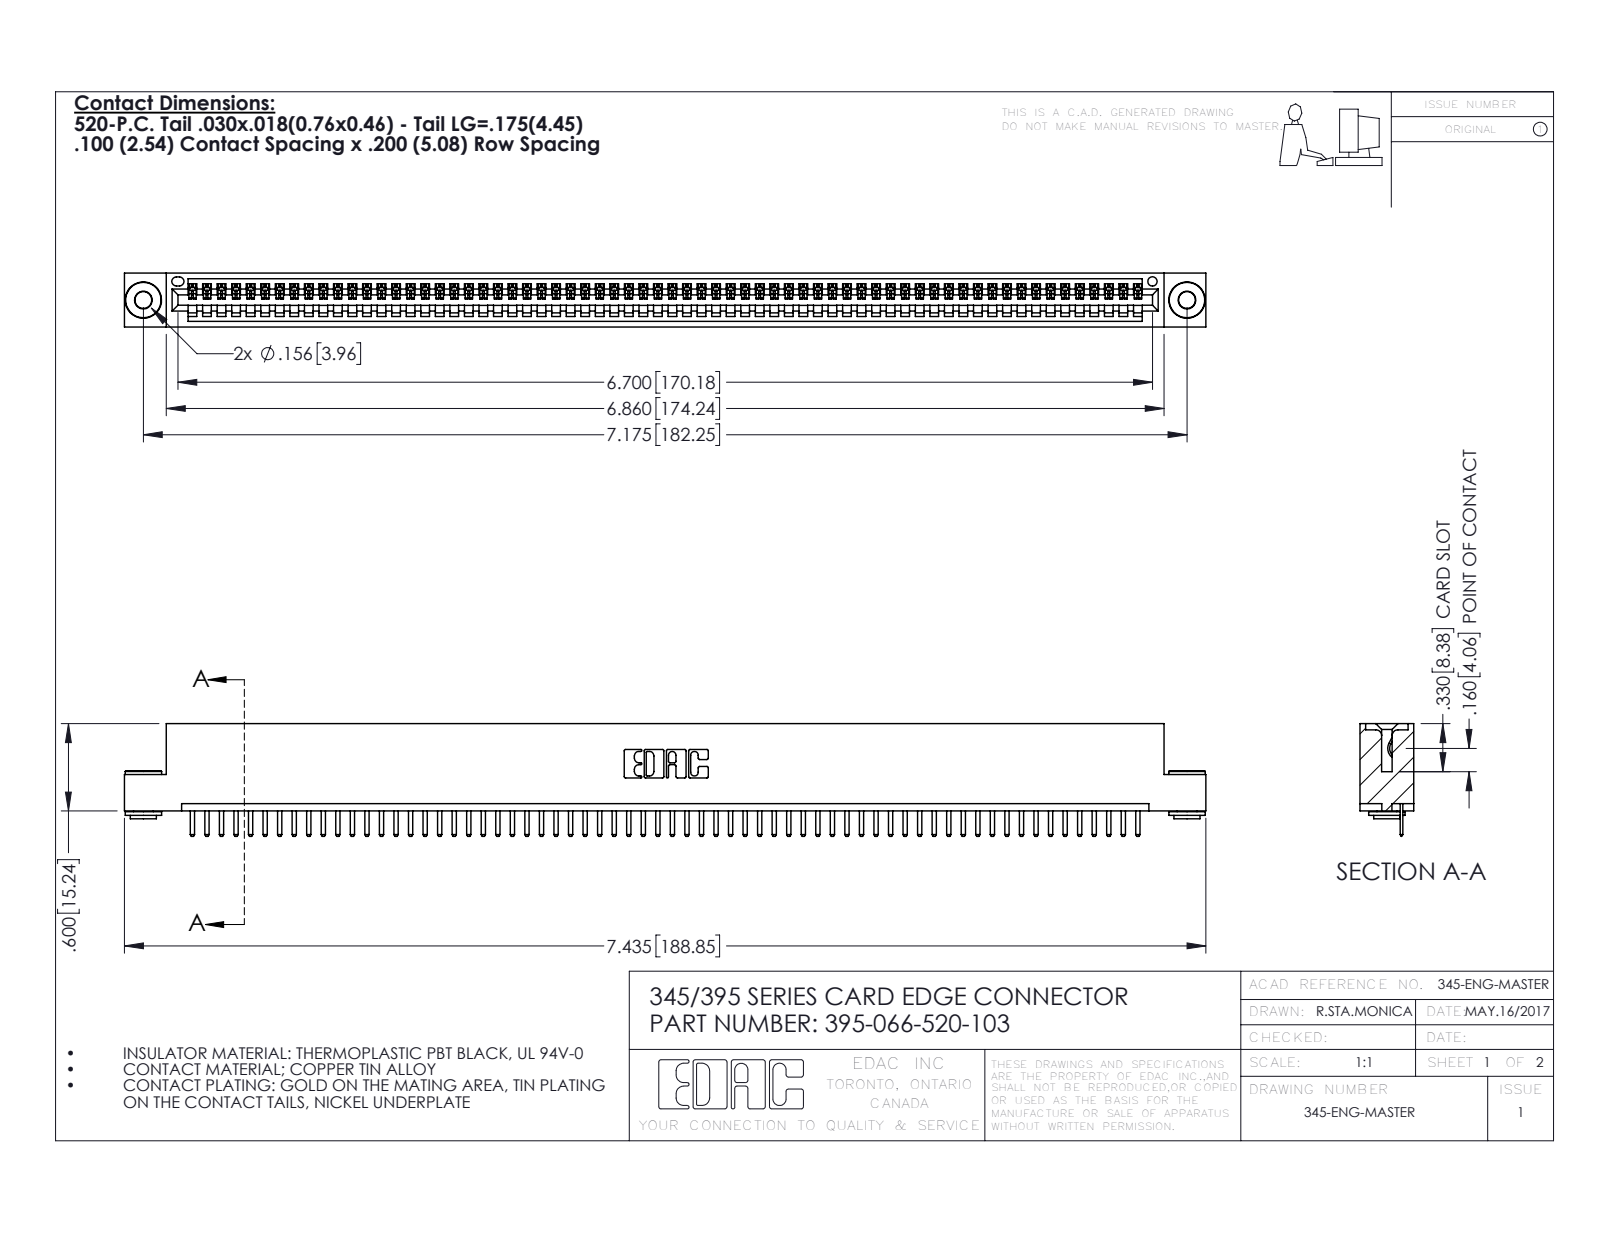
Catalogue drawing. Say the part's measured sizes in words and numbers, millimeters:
The part is named "345-250-002_345-250-002-102; 345-292-001_345-293-120; 345 Part_Flush Mounting Lugs - 0.156 Dia-TH; 395-066-520-103". Its 3-D file was written by "SolidWorks 2016 (CONFIG_CONTROL_DESIGN)". It is 69 solids with 4256 faces: 2862 planar, 1386 cylindrical and 8 other. Overall it measures 188.8 by 19.7 by 9.4 millimeters. Its volume is 17 960 cubic millimeters and its surface area 23 790 square millimeters. Round holes: 2 of diameter 2.9, 2 of diameter 4, 1 of diameter 1.6. Round bosses or shafts: 2 of diameter 6.4, 2 of diameter 4.6, 2 of diameter 3.5. Partial cylindrical surfaces (rounded edges, fillets, slot ends): 134 of radius 0.3, 132 of radius 0.2, 22 of radius 0.3, 6 of radius 0.2, 6 of radius 0.8, 3 of radius 0.7, 2 of radius 0.8, 2 of radius 1. The main face-to-face distances are 1.8, 7.6, 9.4, 5.1, 0.6, 2.5, 6.9, 5.7, 1.8, 3.8. The hole center spacings are 6.9, 176.3, 182.2.
